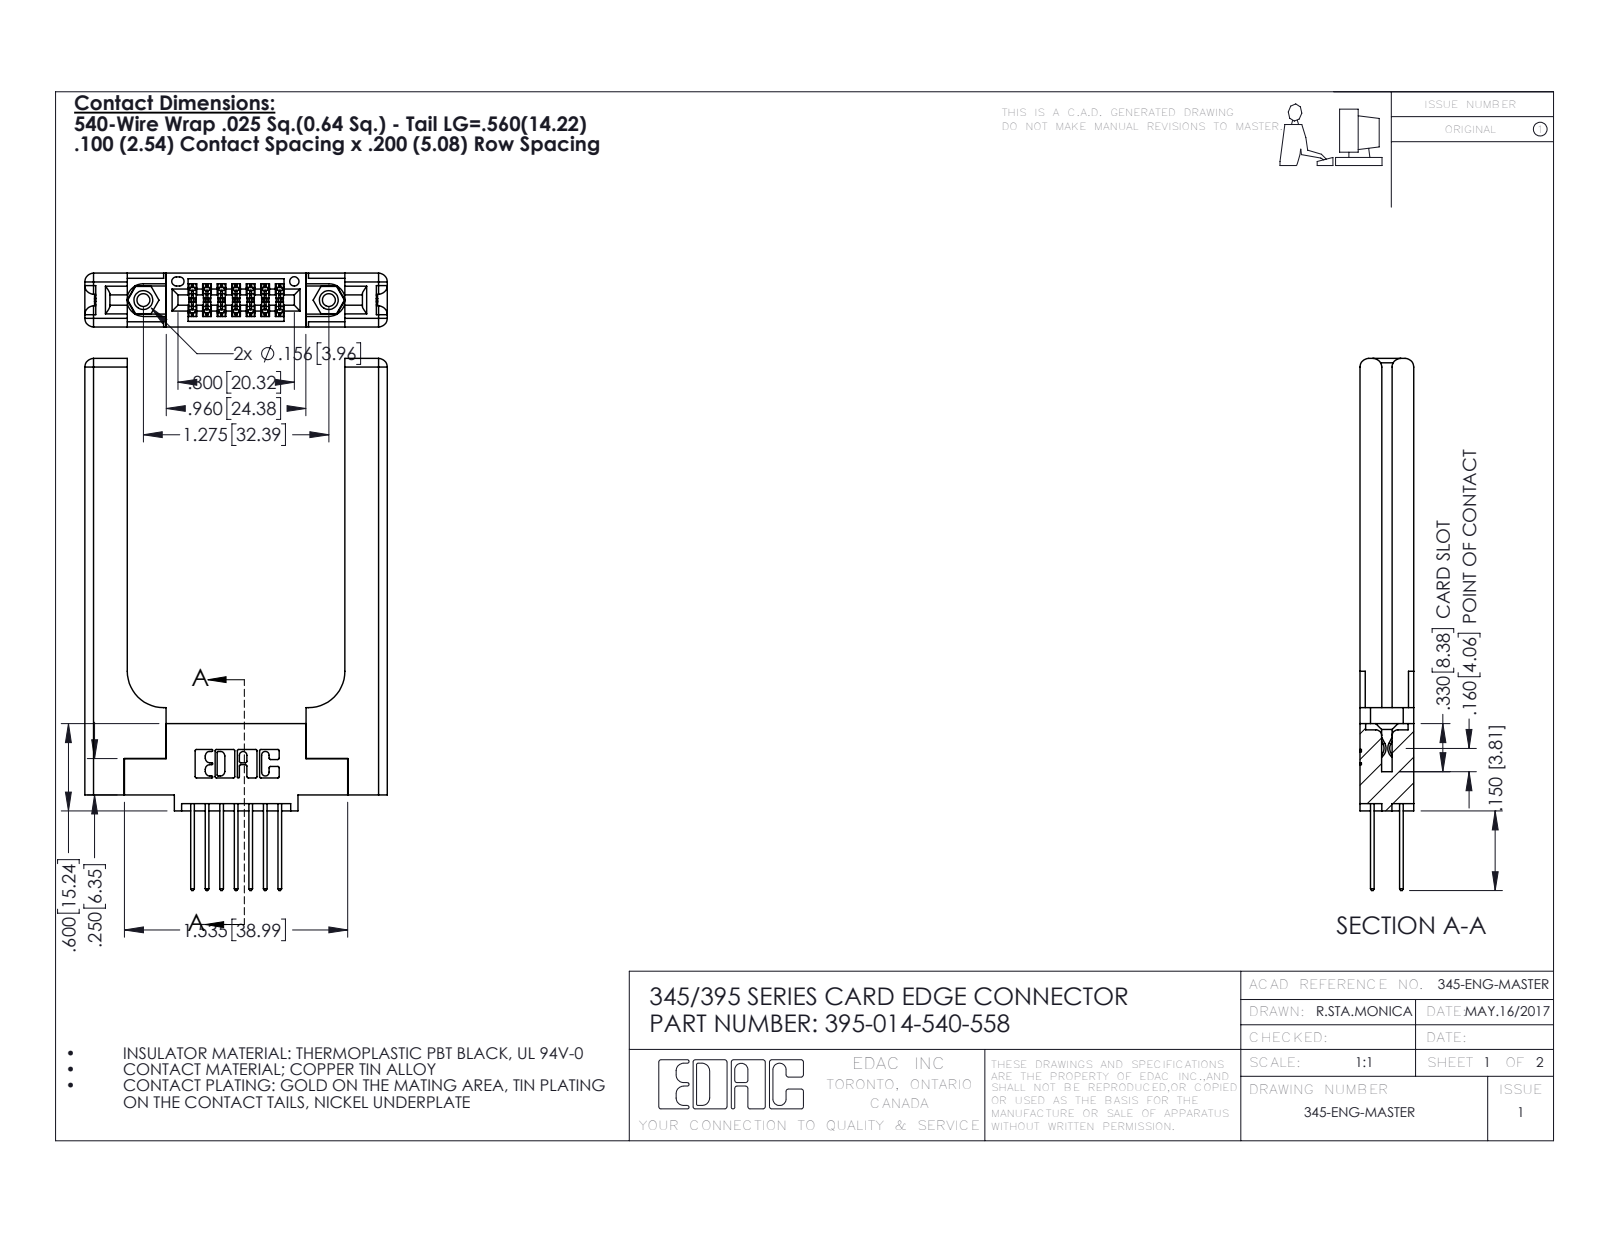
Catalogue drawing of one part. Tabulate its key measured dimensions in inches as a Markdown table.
| quantity | value |
| --- | --- |
| part name | 345 Part_0.110 Offset - 0.156 Dia-TH; 345-220-058_345-220-058; 345-250-001_345-250-001-102; 395-014-540-558 (+1 more) |
| STEP written by | SolidWorks 2016 (CONFIG_CONTROL_DESIGN) |
| units | inches |
| bodies | 19 solids, 1086 faces (694 planar, 332 cylindrical, 60 other) |
| overall size | 3.657 × 2.079 × 0.37 |
| volume | 0.809 in³ |
| surface area | 18.28 in² |
| round holes (diameter × count) | 0.089 × 2, 0.125 × 2, 0.156 × 2, 0.064 × 1 |
| round bosses / shafts (diameter × count) | 0.155 × 2 |
| partial cylindrical surfaces (radius × count) | 0.01 × 22, 0.006 × 21, 0.06 × 16, 0.01 × 14, 0.007 × 6, 0.031 × 6, 0.026 × 3, 0.014 × 2 |
| main face-to-face distances | 0.37, 0.15, 0.072, 0.22, 0.148, 0.077, 0.298, 1.496, 0.225, 0.2 |
| hole center spacings | 0.27, 1.045, 1.275 |
